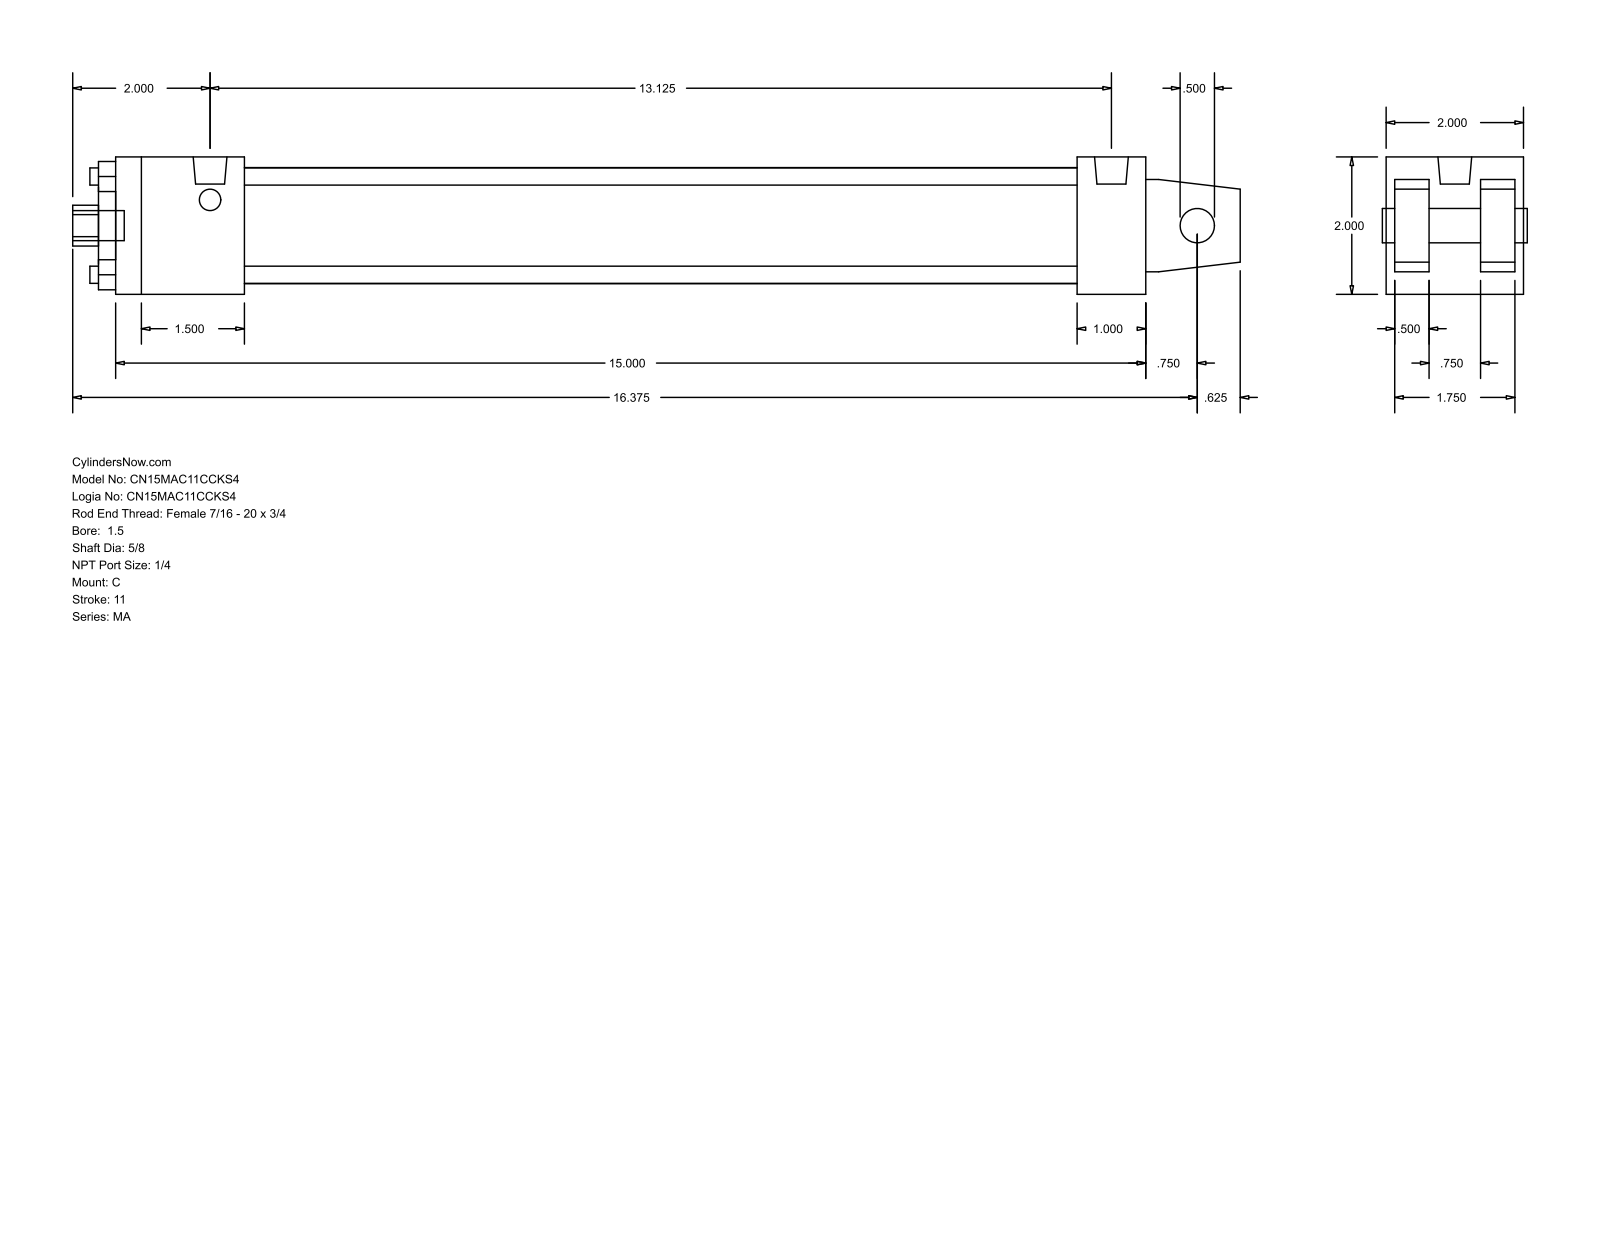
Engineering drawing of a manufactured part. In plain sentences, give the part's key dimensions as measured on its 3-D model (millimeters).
The part is named "MA_C__0150_0.625". Its 3-D file was written by "GSSL Pune (CONFIG_CONTROL_DESIGN)". It is 0 solids with 103 faces: 76 planar, 27 cylindrical and 0 other. Overall it measures 431.8 by 50.8 by 50.8 millimeters. Round holes: 4 of diameter 6.35, 1 of diameter 12.7, 1 of diameter 15.88, 1 of diameter 28.57, 1 of diameter 42.93. Round bosses or shafts: 4 of diameter 7.94, 2 of diameter 12.49, 1 of diameter 11.11. Partial cylindrical surfaces (rounded edges, fillets, slot ends): 1 of radius 7.54. The main face-to-face distances are 50.8, 12.7, 3.17, 15.87, 34.93, 47.63, 31.76, 381, 355.6, 25.4. The hole center spacings are 25.68, 36.32, 51.36.
